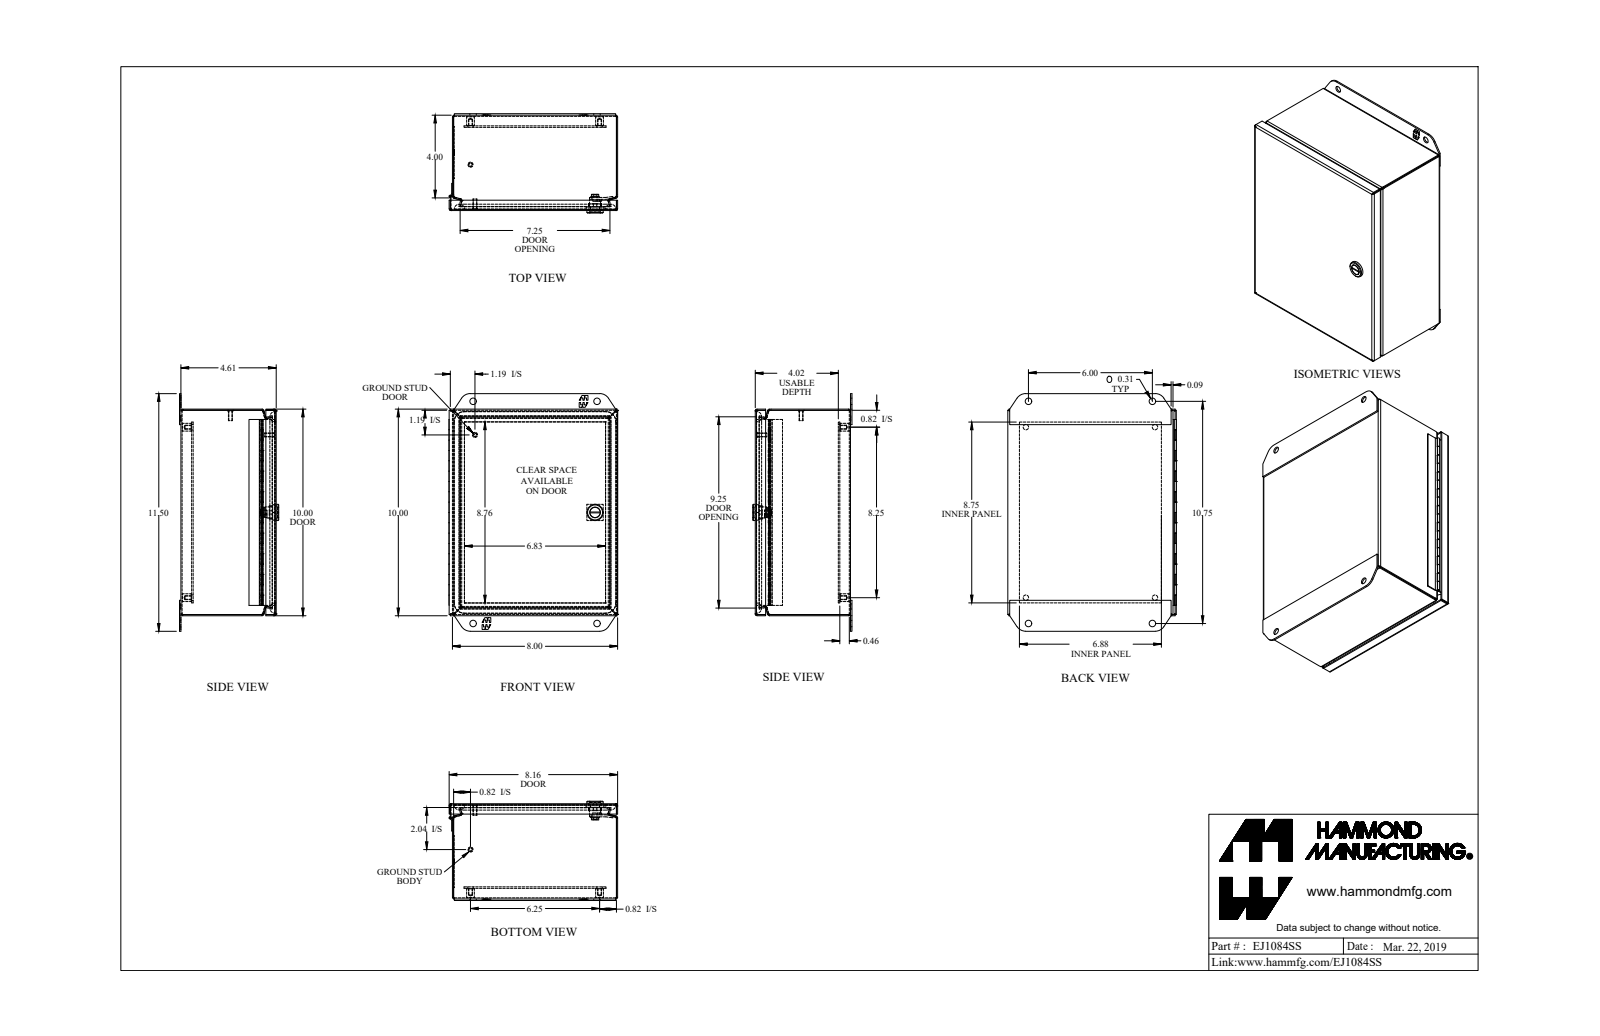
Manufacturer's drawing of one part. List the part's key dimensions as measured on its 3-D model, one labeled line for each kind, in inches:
Part name (STEP PRODUCT): EJ1084SS_Default
STEP written by: SolidWorks 2019 (CONFIG_CONTROL_DESIGN)
Units: inches
Bodies: 16 solids, 688 faces (386 planar, 206 cylindrical, 96 other)
Overall size (bounding box): 11.5 × 8.165 × 4.805
Volume: 29.37 in³ · Surface area: 966.4 in²
Round holes (diameter × count): ⌀0.156 ×4, ⌀0.265 ×4, ⌀0.313 ×4, ⌀0.05 ×1, ⌀0.516 ×1
Round bosses / shafts (diameter × count): ⌀0.375 ×4, ⌀0.25 ×2, ⌀0.19 ×2, ⌀0.788 ×1, ⌀0.535 ×1, ⌀0.496 ×1, ⌀0.435 ×1, ⌀0.1 ×1
Partial cylindrical surfaces — rounded edges, fillets, slot ends (radius × count): R0.029 ×16, R0.086 ×16, R0.281 ×12, R0.25 ×4, R0.499 ×4, R0.5 ×4, R0.06 ×2, R0.03 ×1
Main face-to-face distances: 0.057, 4.554, 0.072, 0.589, 4.611, 4.497, 7.943, 9.943, 4.094, 4.037
Hole centre spacings: 1.257, 9.501, 8.25, 4.131, 6.252, 10.35, 11.304, 5.376
